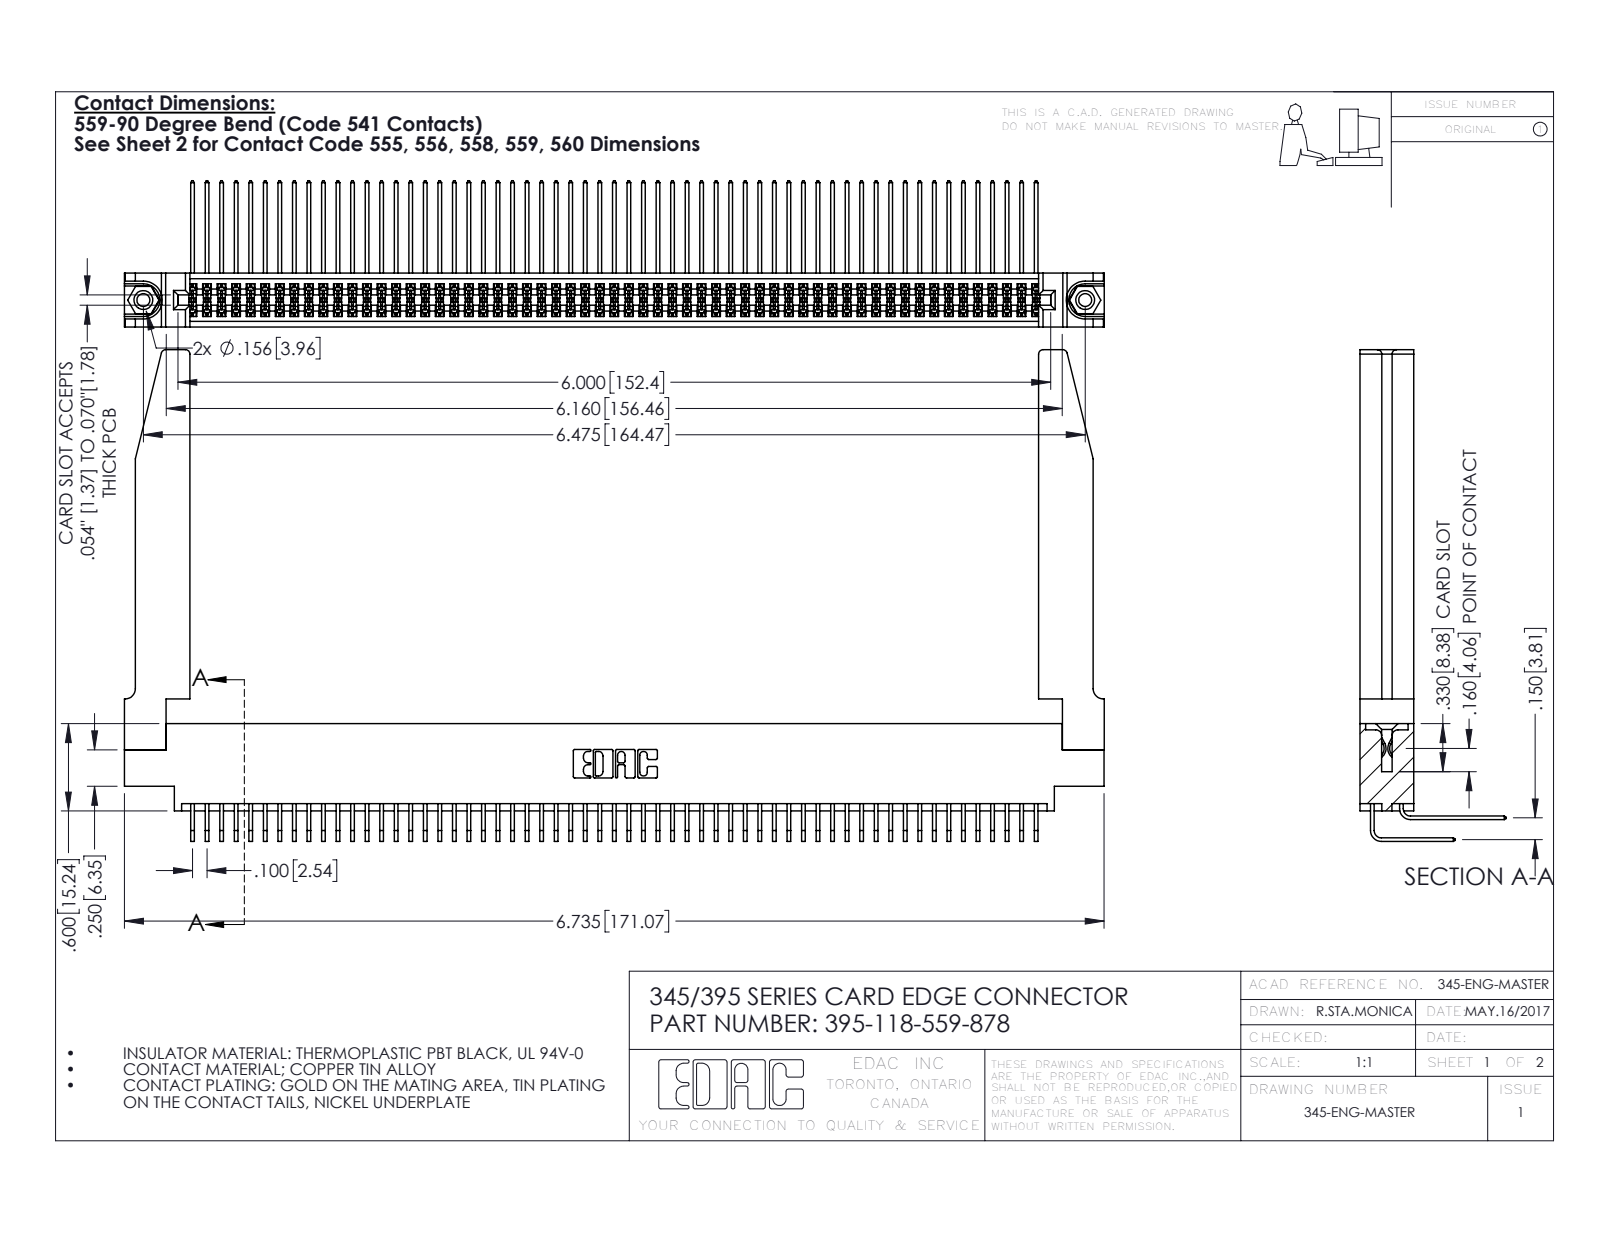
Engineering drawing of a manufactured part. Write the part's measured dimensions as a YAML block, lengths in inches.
part_name: "395-118-559-878; 345-250-001_345-250-001-102; 345-292-001_558 559 Tail - 1; 345 Part_0.170 Offset - 0.156 Dia-TH (+2 more)"
step_written_by: "SolidWorks 2016 (CONFIG_CONTROL_DESIGN)"
units: inches
bodies: {solids: 123, faces: 6500, planar: 4356, cylindrical: 2092, other: 52}
overall_size: [6.736, 3.379, 1.005]
volume: 1.533
surface_area: 56.03
round_holes:
  - {diameter: 0.089, count: 2}
  - {diameter: 0.125, count: 2}
  - {diameter: 0.156, count: 2}
  - {diameter: 0.064, count: 1}
round_bosses_or_shafts:
  - {diameter: 0.155, count: 2}
partial_cylinders:
  - {radius: 0.006, count: 177}
  - {radius: 0.01, count: 22}
  - {radius: 0.03, count: 8}
  - {radius: 0.007, count: 6}
  - {radius: 0.031, count: 6}
  - {radius: 0.026, count: 3}
  - {radius: 0.014, count: 2}
  - {radius: 0.019, count: 2}
face_to_face_distances: [0.072, 0.37, 0.298, 0.098, 0.272, 0.025, 0.2, 0.225, 0.15, 0.175]
hole_center_spacings: [0.27, 6.239, 6.475]
